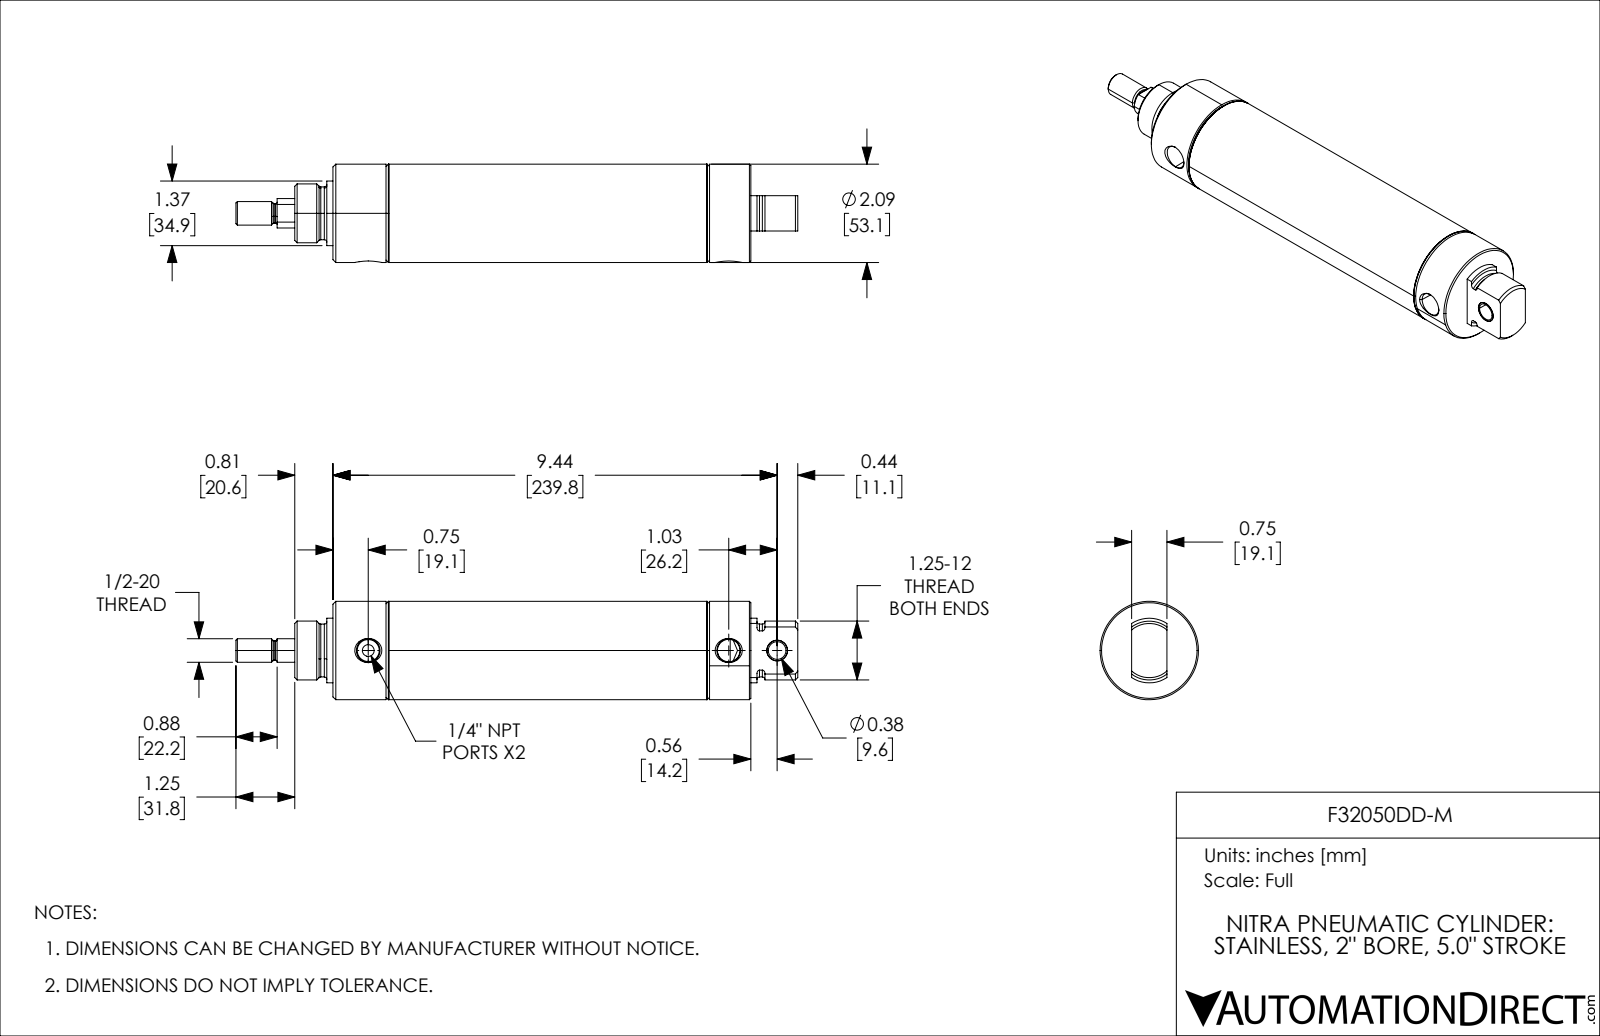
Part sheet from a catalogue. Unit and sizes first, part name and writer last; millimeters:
Units: millimetres
Overall size (bounding box): 303.23 × 53.09 × 53.09
Round holes (diameter × count): ⌀6.35 ×1, ⌀9.55 ×1, ⌀11.15 ×1, ⌀12.18 ×1, ⌀16.52 ×1, ⌀19.05 ×1, ⌀49.05 ×1
Round bosses / shafts (diameter × count): ⌀53.09 ×1, ⌀51.16 ×1, ⌀34.87 ×1, ⌀31.75 ×1, ⌀28.51 ×1, ⌀15.88 ×1, ⌀12.7 ×1, ⌀10.46 ×1
Partial cylindrical surfaces — rounded edges, fillets, slot ends (radius × count): R14.25 ×1
Main face-to-face distances: 30.18, 127, 157.18, 187.4, 60.4, 30.22, 38.15, 165.15, 195.33, 225.55
Hole centre spacings: 26.17, 194.56, 220.73
Volume: 280 970 mm³ · Surface area: 109 977 mm²
Bodies: 5 solids, 160 faces (31 planar, 60 cylindrical, 69 other)
Part name (STEP PRODUCT): F32050DD-M_11; F32050DD-M_5; F32050DD-M_3; F32050DD-M (+2 more)
STEP written by: SolidWorks 2021 (CONFIG_CONTROL_DESIGN)
